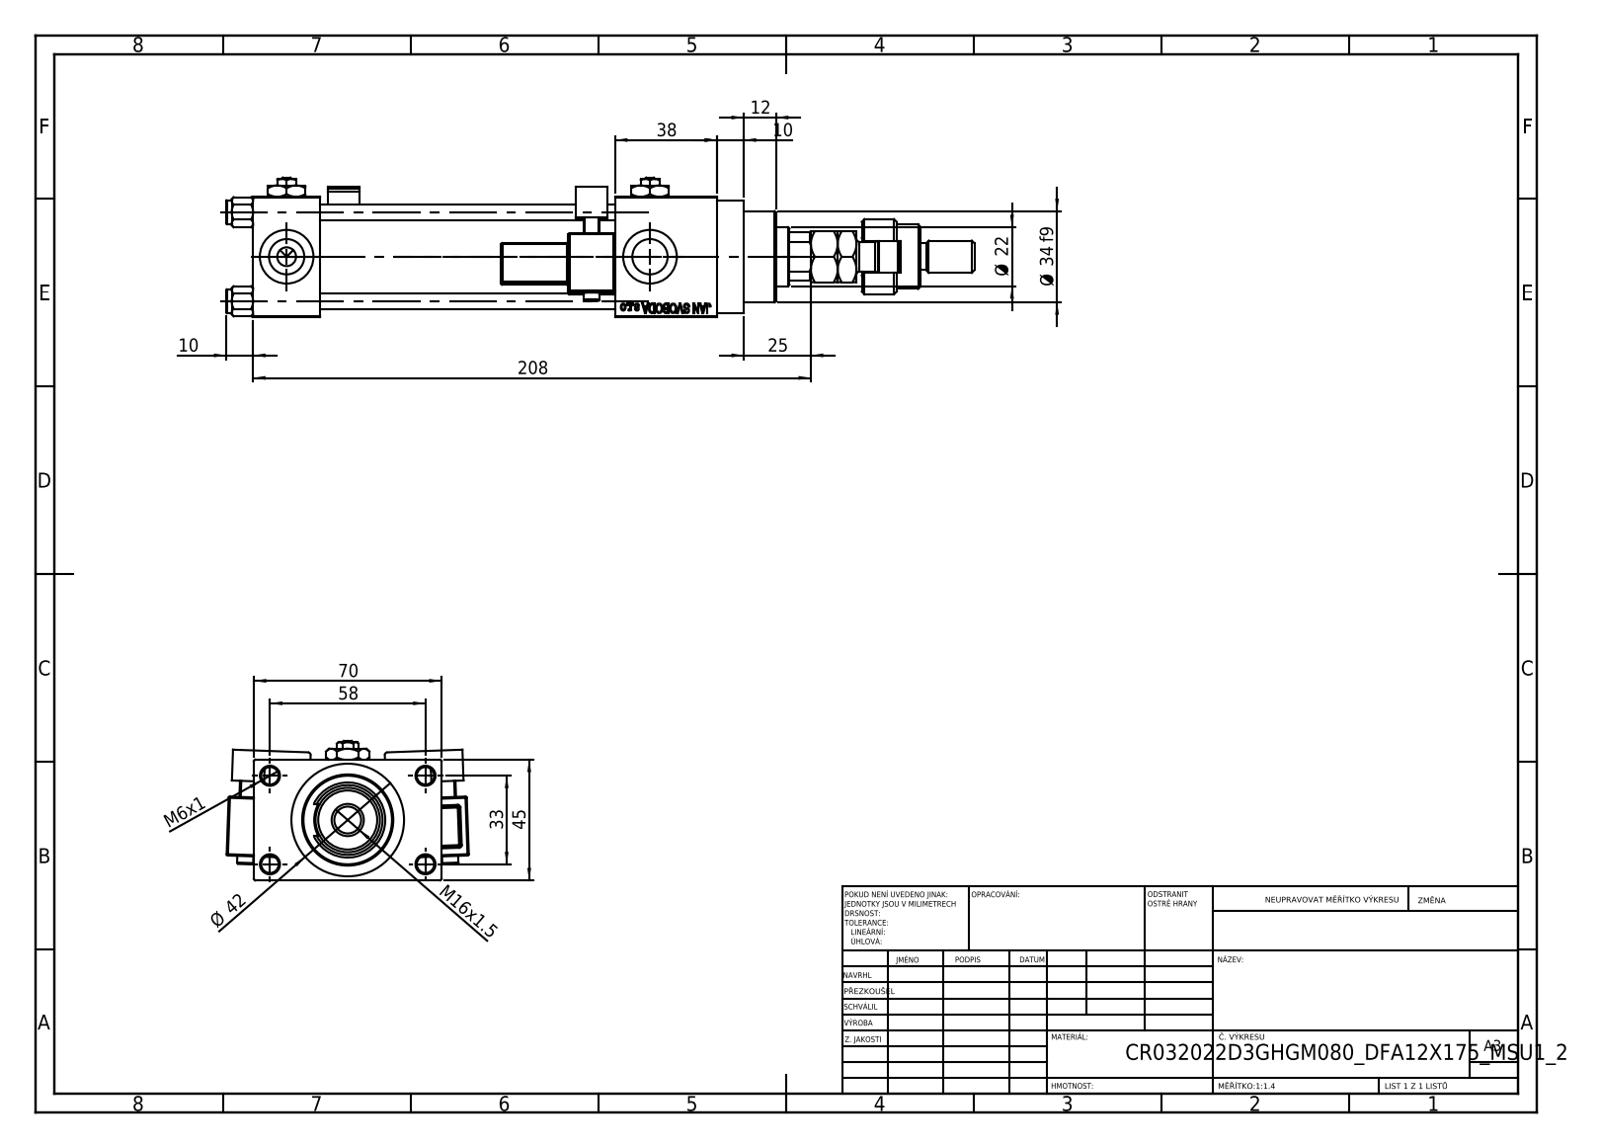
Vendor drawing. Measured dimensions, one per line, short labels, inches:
name: V215CR_VCP_D; FEMALE_PART_FOR_DFA; V215_VC_A; NUT_M5_D (+5 more)
written by: SolidWorks 2019 (CONFIG_CONTROL_DESIGN)
unit: in
bodies: 17 solids, 1444 faces (632 planar, 172 cylindrical, 640 other)
size: 10.984 × 3.556 × 2.047
volume: 21.34 in³; area: 190.2 in²
holes: 4× ⌀0.236, 4× ⌀0.256, 4× ⌀0.518, 4× ⌀0.787, 3× ⌀0.276, 1× ⌀0.413, 1× ⌀0.866, 1× ⌀0.945, 1× ⌀0.984, 1× ⌀1.26, 1× ⌀1.299
bosses: 4× ⌀0.354, 2× ⌀0.236, 1× ⌀1.654, 1× ⌀1.496, 1× ⌀1.339, 1× ⌀1.102, 1× ⌀0.709, 1× ⌀0.472
rounds: 48× R0.02, 2× R0.039, 2× R0.098, 2× R0.157, 1× R0.384, 1× R0.413
face distances: 1.772, 0.984, 4.331, 0.492, 0.118, 5.315, 2.264, 5.827, 1.496, 6.811
hole spacings: 0.488, 0.924, 1.307, 1.314, 1.392, 1.795, 2.219, 1.299
